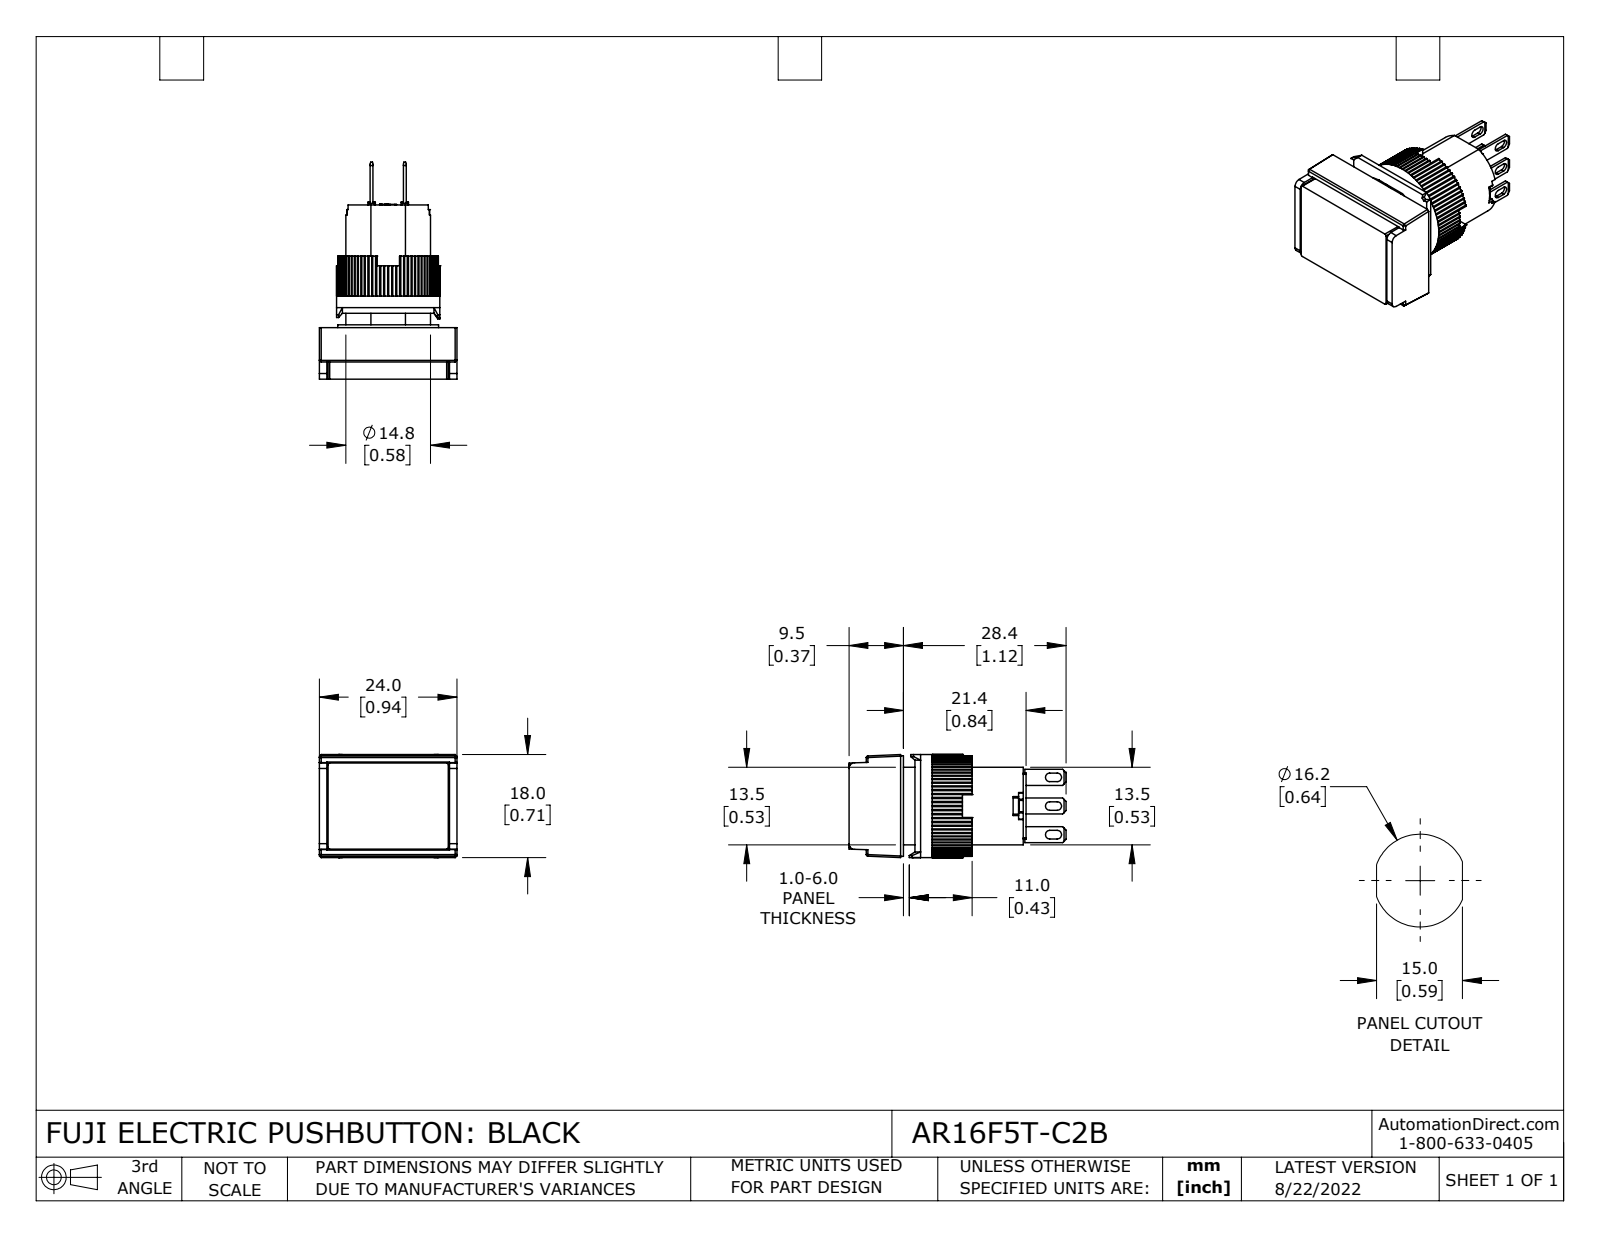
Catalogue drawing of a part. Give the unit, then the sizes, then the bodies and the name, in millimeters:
Units: millimetres
Overall size (bounding box): 37.9 × 24 × 18
Round holes (diameter × count): ⌀13.8 ×1, ⌀14.8 ×1
Round bosses / shafts (diameter × count): ⌀18 ×1, ⌀17.6 ×1
Partial cylindrical surfaces — rounded edges, fillets, slot ends (radius × count): R0.3 ×80, R0.2 ×12, R0.3 ×6, R0.8 ×6, R1 ×2
Main face-to-face distances: 5.4, 9, 3.6, 12.5, 8.9, 3.5, 0.5, 21.4, 1.5, 11.5
Volume: 7 260 mm³ · Surface area: 5 886 mm²
Bodies: 12 solids, 813 faces (632 planar, 177 cylindrical, 4 other)
Part name (STEP PRODUCT): AR16F5T-C2B
STEP written by: SolidWorks 2021 (CONFIG_CONTROL_DESIGN)
